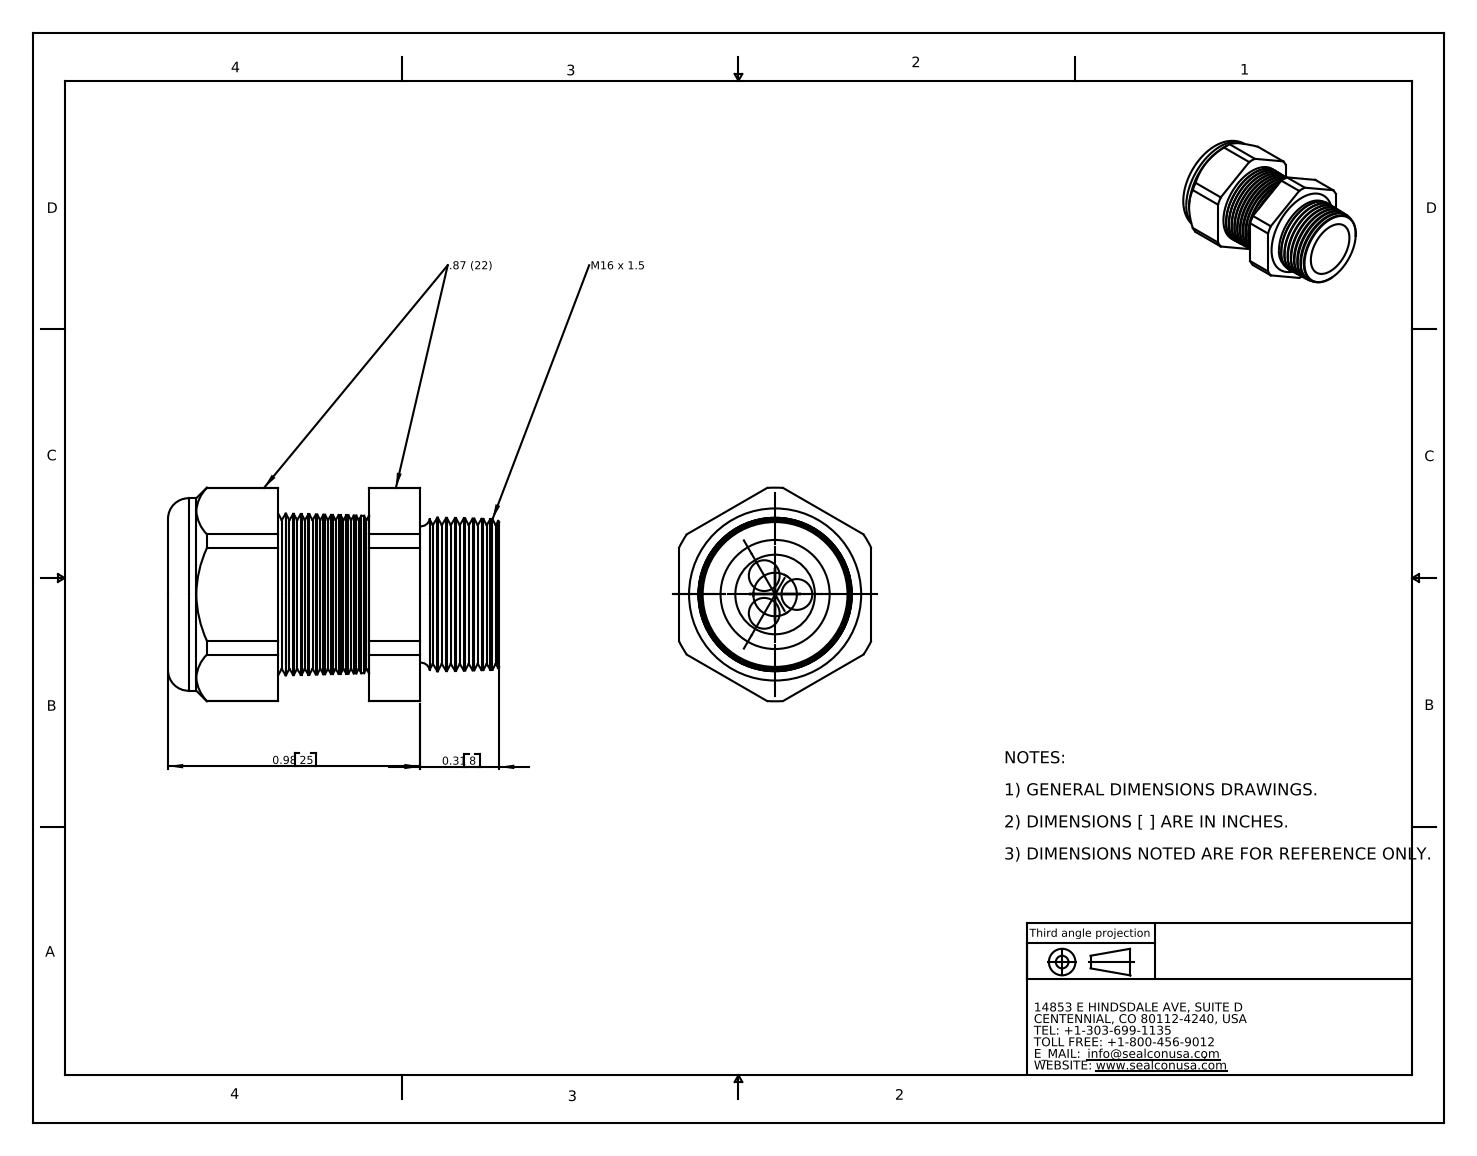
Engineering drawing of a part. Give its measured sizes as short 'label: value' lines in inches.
name: CD17M2-BK
written by: SolidWorks 2007 (CONFIG_CONTROL_DESIGN)
unit: in
bodies: 2 solids, 185 faces (21 planar, 26 cylindrical, 138 other)
size: 1.29 × 0.833 × 0.75
volume: 0.352 in³; area: 6.679 in²
holes: 3× ⌀0.12, 1× ⌀0.29, 1× ⌀0.31
bosses: 1× ⌀0.75
rounds: 1× R0.416
face distances: 0.75, 0.75, 0.783, 0.429, 0.354, 0.98, 0.551, 0.197, 1.29, 0.861
hole spacings: 0.085, 0.147, 0.146
